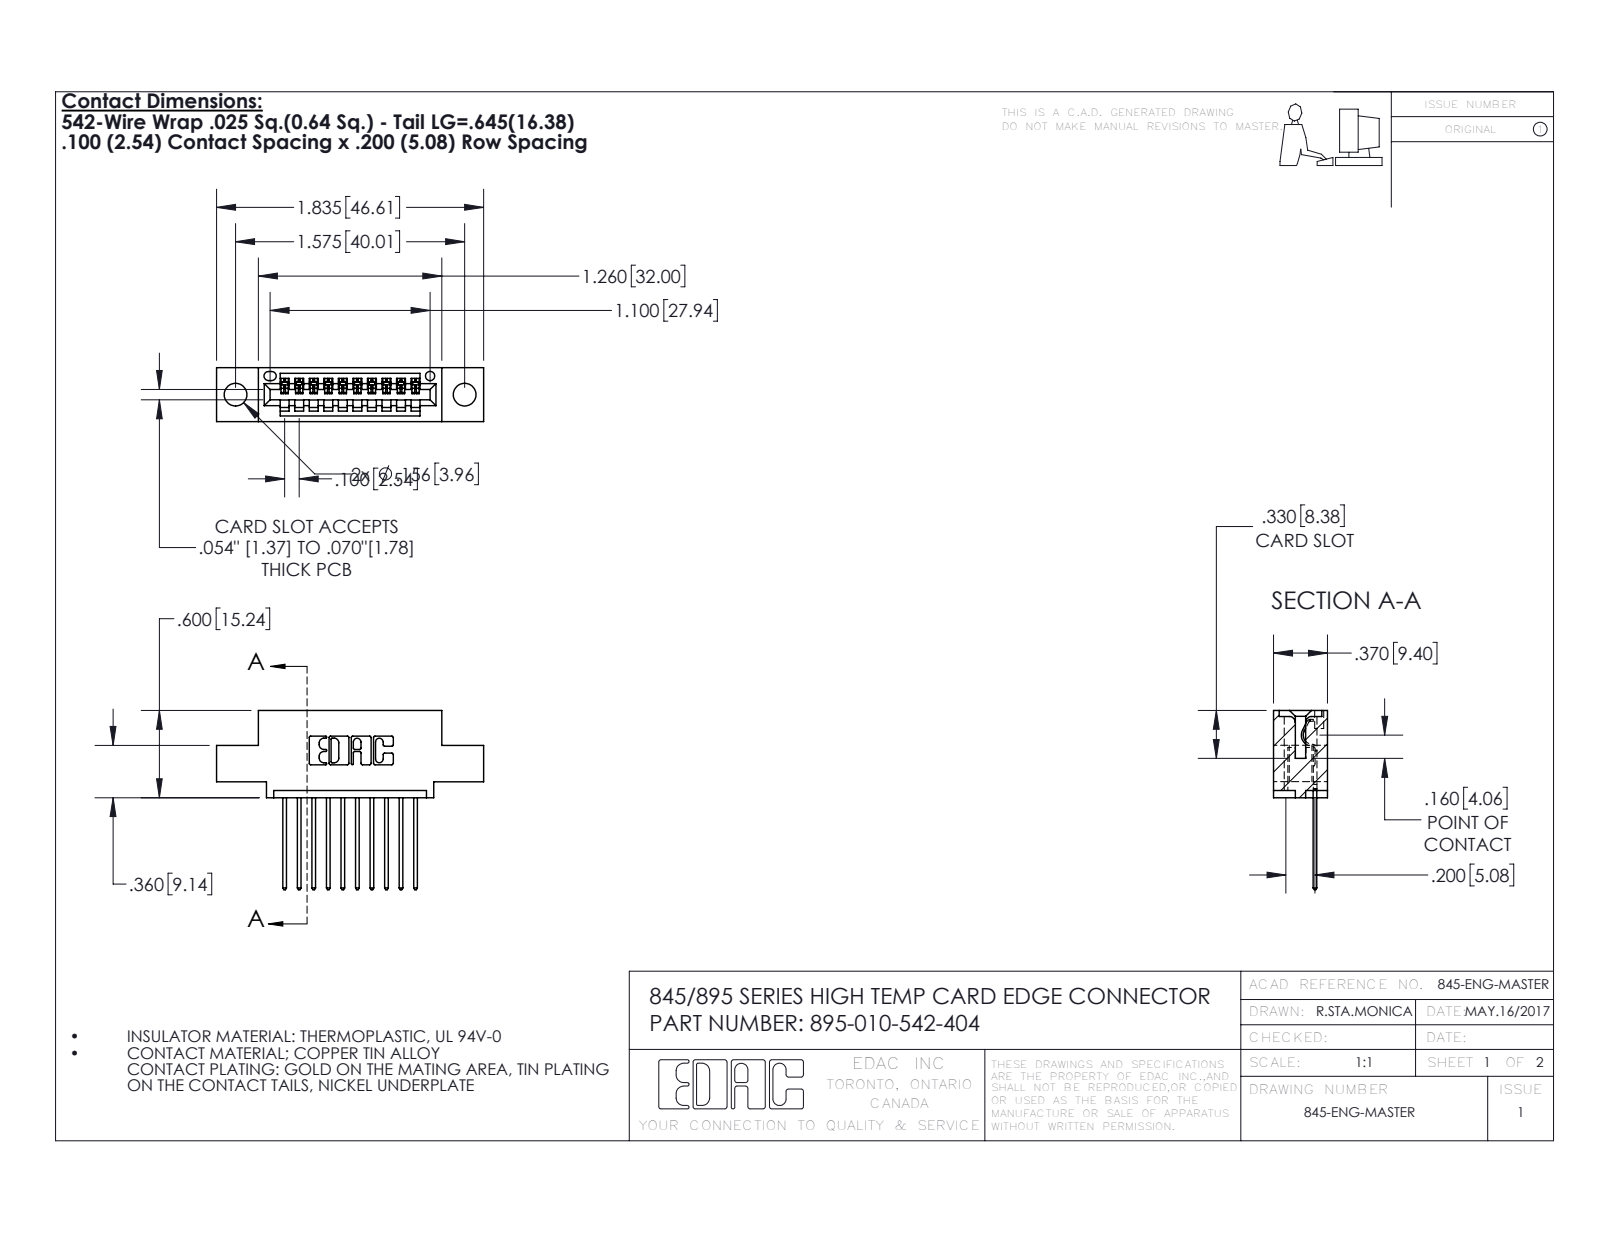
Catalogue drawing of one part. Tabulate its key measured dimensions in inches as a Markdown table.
| quantity | value |
| --- | --- |
| part name | 345-292-001_345-293-142; 345 Part_0.110 Offset - 0.156 Dia-TH; 395-010-542-404 |
| STEP written by | SolidWorks 2016 (CONFIG_CONTROL_DESIGN) |
| units | inches |
| bodies | 11 solids, 710 faces (484 planar, 226 cylindrical, 0 other) |
| overall size | 1.835 × 1.232 × 0.37 |
| volume | 0.246 in³ |
| surface area | 7.667 in² |
| round holes (diameter × count) | 0.156 × 2, 0.064 × 1 |
| partial cylindrical surfaces (radius × count) | 0.01 × 22, 0.006 × 20, 0.01 × 20, 0.007 × 6, 0.031 × 6, 0.026 × 3, 0.031 × 2, 0.04 × 2 |
| main face-to-face distances | 0.298, 0.072, 0.2, 0.37, 0.098, 0.272, 0.025, 0.1, 0.6, 0.06 |
| hole center spacings | 0.27, 1.344, 1.575 |
